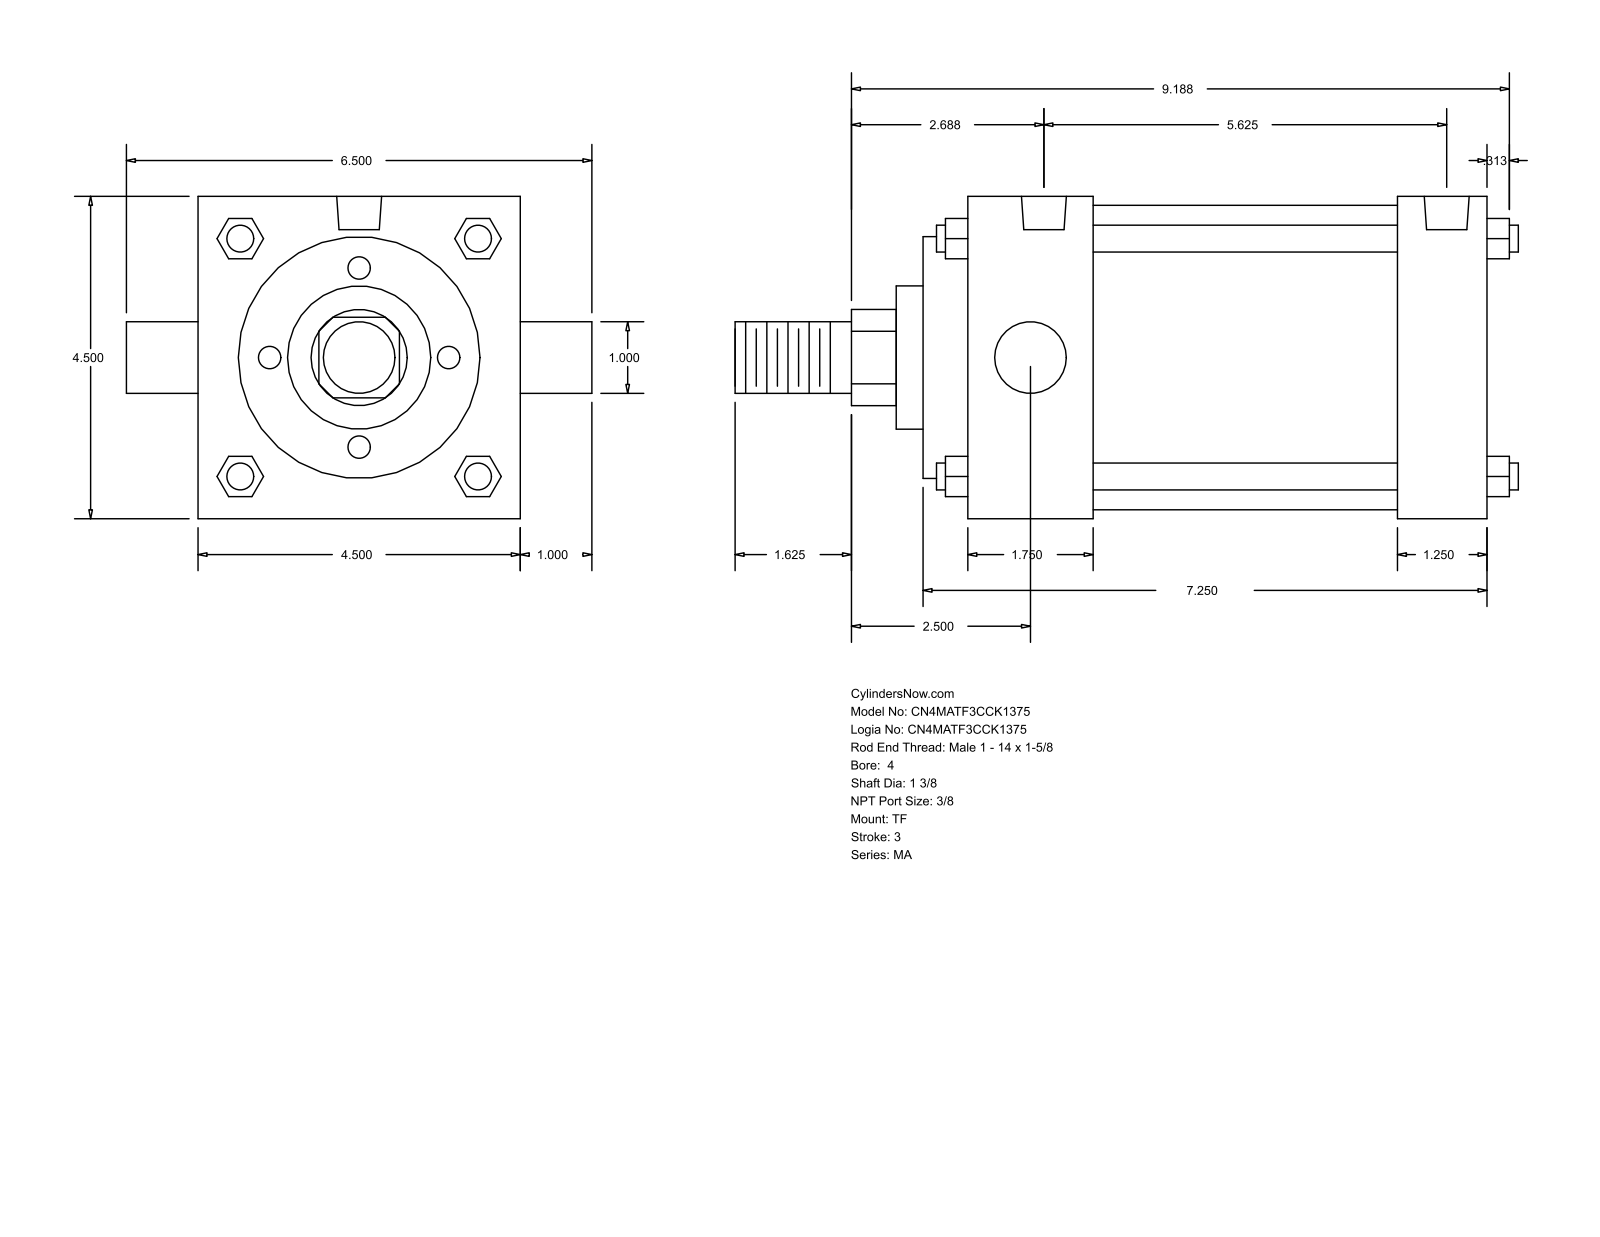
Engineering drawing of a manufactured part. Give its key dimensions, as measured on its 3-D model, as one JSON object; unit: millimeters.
{"part_name": "MA_TF__0400_1.375", "step_written_by": "GSSL Pune (CONFIG_CONTROL_DESIGN)", "units": "millimeters", "bodies": {"solids": 0, "faces": 122, "planar": 93, "cylindrical": 29, "other": 0}, "overall_size": [277.81, 165.1, 114.3], "round_holes": [[11.11, 3], [15.93, 2]], "round_bosses_or_shafts": [[9.53, 4], [25.4, 2], [107.95, 1], [85.72, 1], [50.8, 1], [34.92, 1]], "partial_cylinders_radius": [[17.06, 1]], "face_to_face_distances": [114.3, 184.16, 15.87, 200.03, 168.28, 152.41, 31.75, 60.32, 44.45, 107.96], "hole_center_spacings": [4.76, 4.77, 133.35, 138.11, 138.12, 142.88]}
